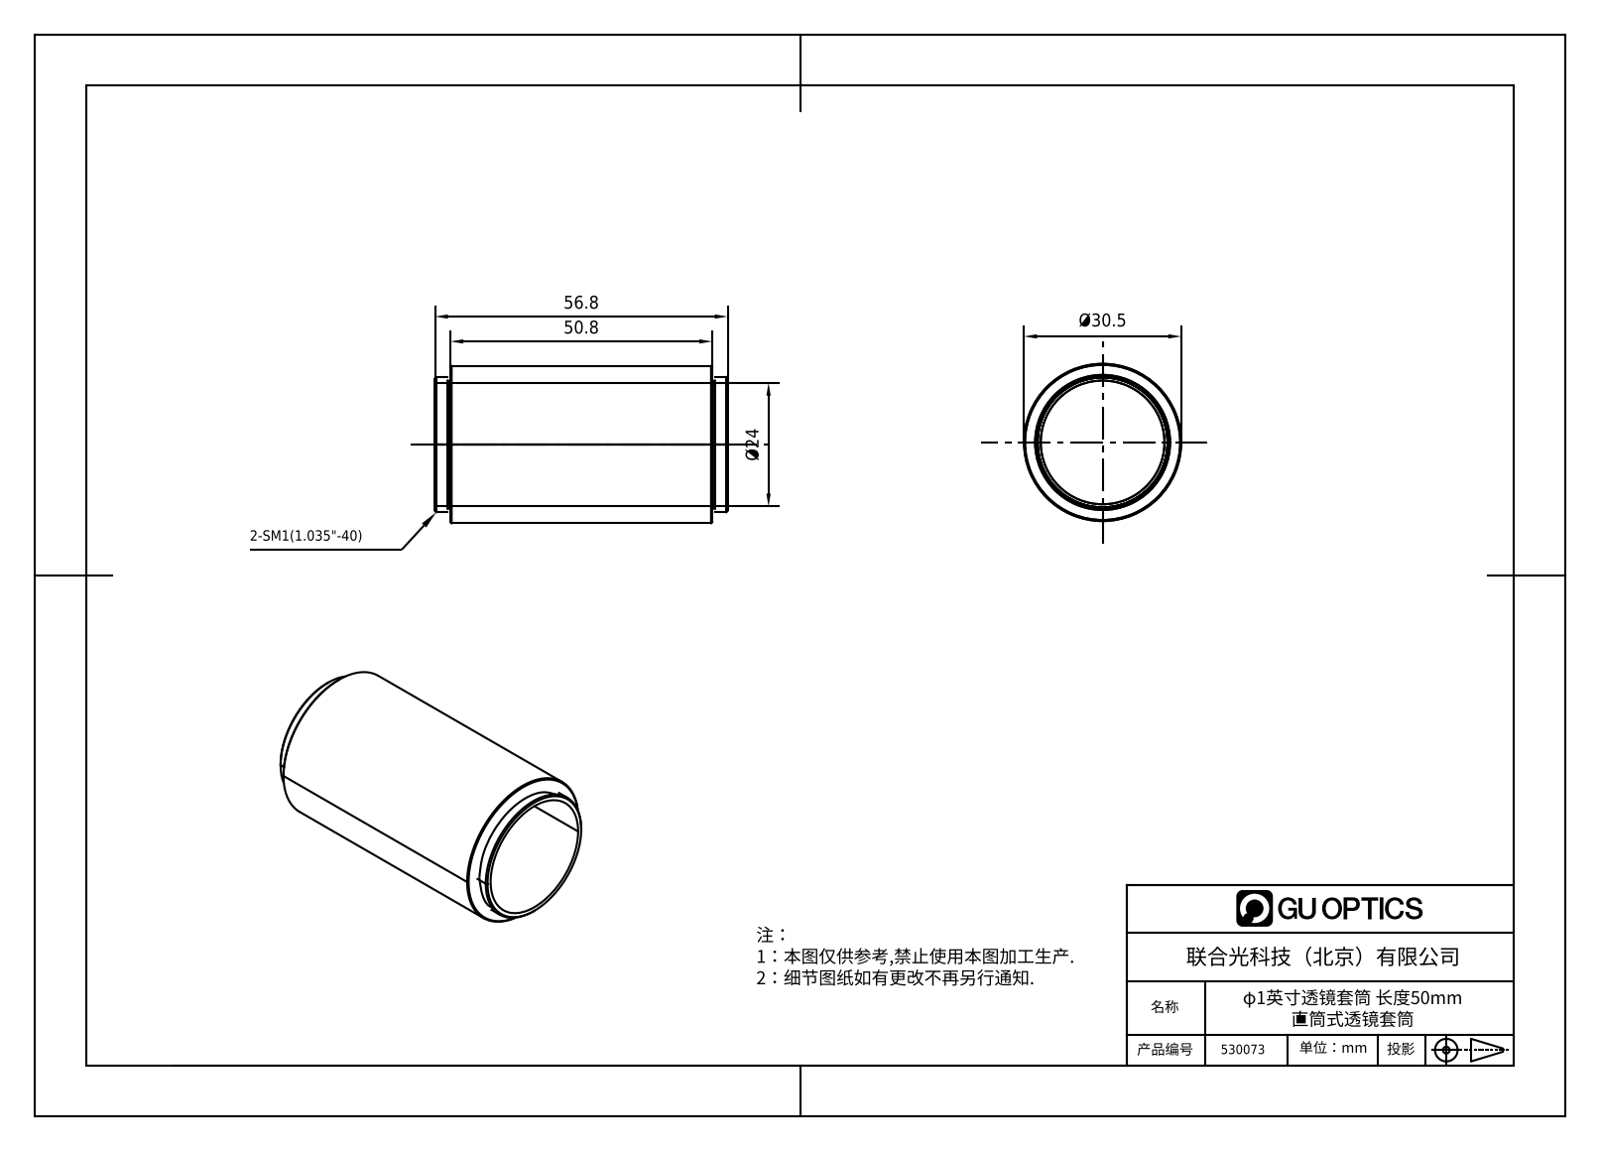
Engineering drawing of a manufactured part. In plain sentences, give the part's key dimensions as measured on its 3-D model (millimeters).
The part is named "1.7.5.3_ZTJ-1-2.0_SM1标准型2.0英寸间隔式透镜套筒". Its 3-D file was written by "SolidWorks 2018 (AUTOMOTIVE_DESIGN)". It is 0 solids with 24 faces: 4 planar, 12 cylindrical and 8 other. Overall it measures 56.8 by 30.5 by 30.5 millimeters. Round holes: 1 of diameter 24. Round bosses or shafts: 1 of diameter 30.5, 1 of diameter 26.2, 1 of diameter 25.2. The main face-to-face distances are 50.8, 3, 53.8, 56.8.
